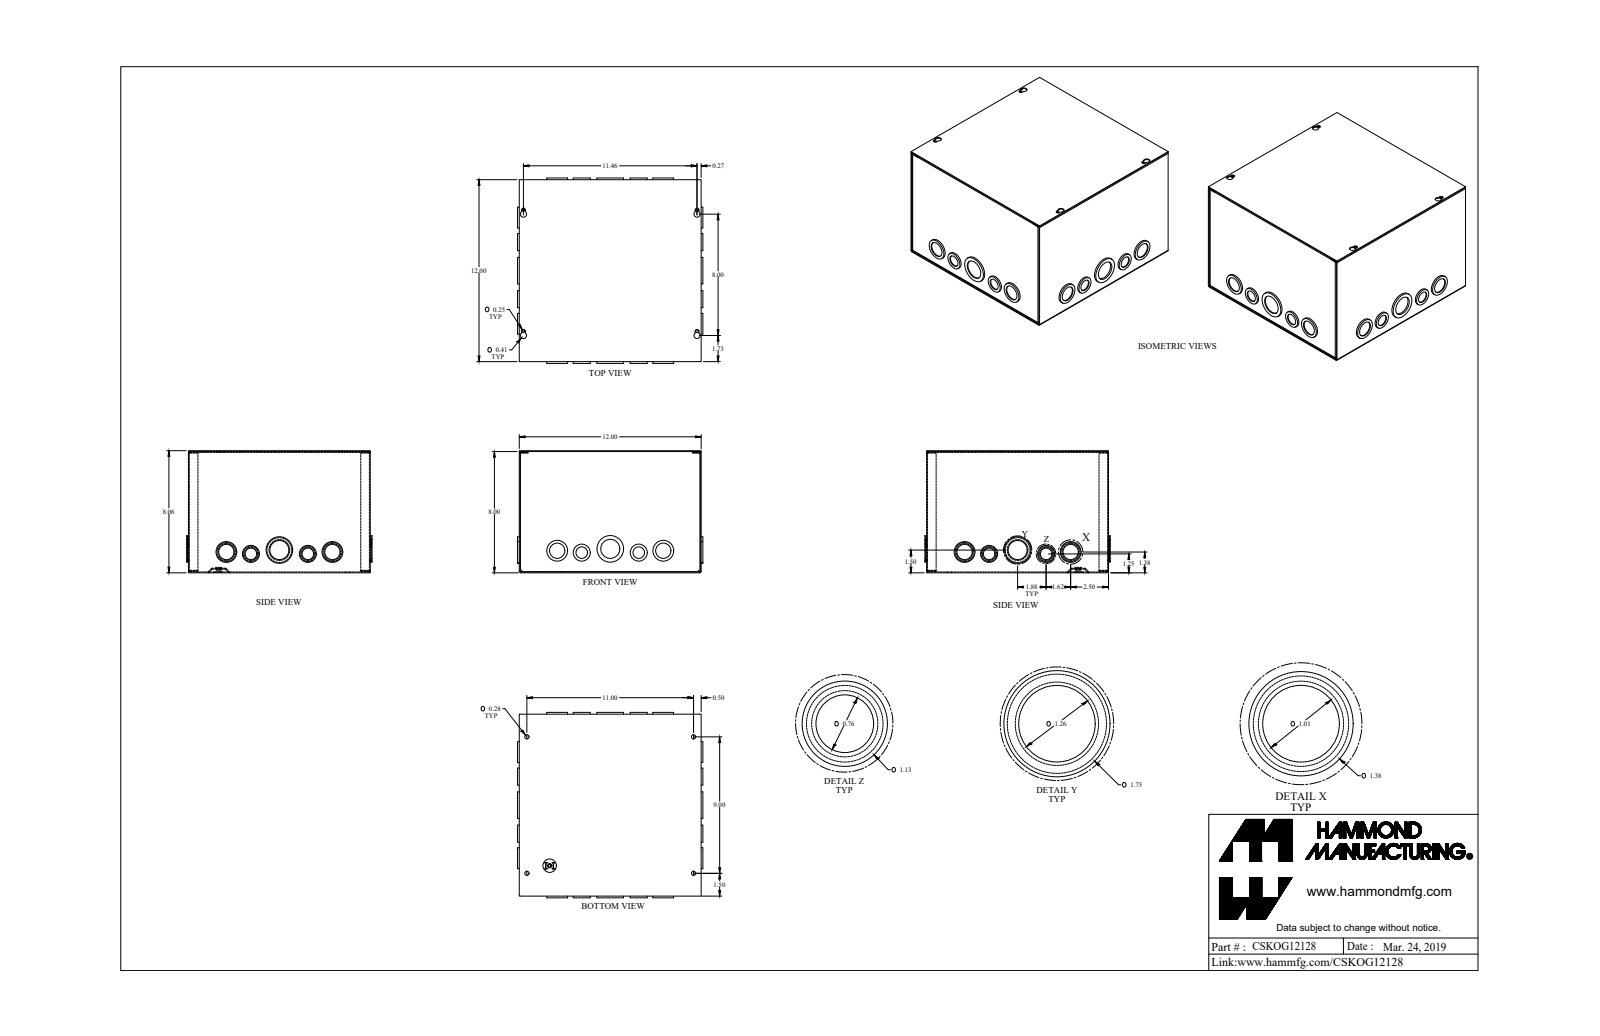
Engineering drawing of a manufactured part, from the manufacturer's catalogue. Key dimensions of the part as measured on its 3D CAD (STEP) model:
Part name (STEP PRODUCT): CSKOG12128_Default
STEP written by: SolidWorks 2019 (CONFIG_CONTROL_DESIGN)
Units: inches
Bodies: 4 solids, 445 faces (205 planar, 232 cylindrical, 8 other)
Overall size (bounding box): 12.234 × 12.234 × 8.057
Volume: 41.47 in³ · Surface area: 1 468 in²
Round holes (diameter × count): ⌀1.011 ×8, ⌀1.261 ×6, ⌀0.17 ×5, ⌀0.281 ×4, ⌀0.761 ×4, ⌀1.636 ×2, ⌀0.5 ×1
Round bosses / shafts (diameter × count): ⌀1.125 ×6, ⌀1.375 ×5, ⌀0.875 ×4, ⌀0.875 ×4, ⌀1.75 ×2, ⌀1.125 ×2, ⌀1.375 ×1, ⌀0.492 ×1
Partial cylindrical surfaces — rounded edges, fillets, slot ends (radius × count): R0.029 ×12, R0.086 ×12, R0.057 ×8, R0.125 ×4, R0.203 ×4
Main face-to-face distances: 0.057, 11.943, 8, 12, 11.886, 7.943, 8.057, 0.07, 11.873, 0.114
Hole centre spacings: 0.55, 1.625, 1.896, 3.502, 5.381, 8.503, 11.241, 14.084
